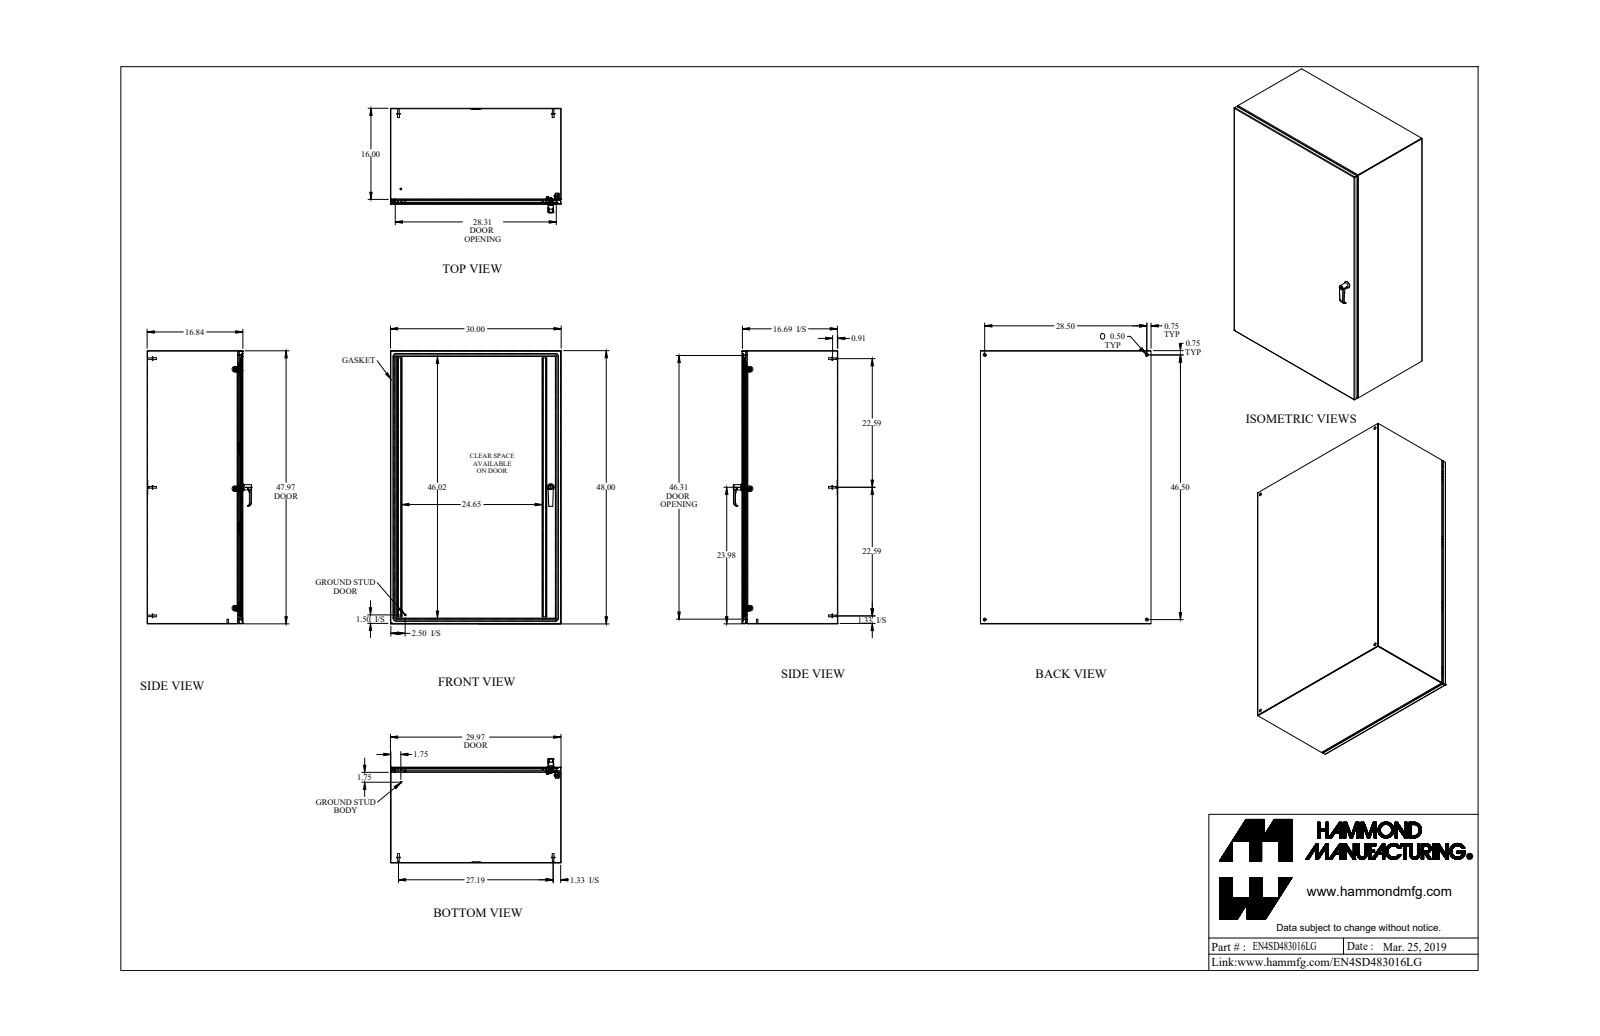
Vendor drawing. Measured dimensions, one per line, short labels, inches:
name: EN4SD483016LG
written by: SolidWorks 2018 (AUTOMOTIVE_DESIGN)
unit: in
bodies: 54 solids, 1427 faces (628 planar, 526 cylindrical, 273 other)
size: 48 × 30 × 18.367
volume: 439.2 in³; area: 12 206 in²
holes: 6× ⌀0.176, 4× ⌀0.5, 3× ⌀0.196, 3× ⌀0.25, 3× ⌀0.265, 3× ⌀0.413, 2× ⌀0.256, 2× ⌀0.313, 2× ⌀0.394, 1× ⌀0.172, 1× ⌀0.24, 1× ⌀0.242
bosses: 7× ⌀0.25, 6× ⌀0.375, 6× ⌀0.156, 5× ⌀0.625, 5× ⌀0.313, 5× ⌀0.27, 3× ⌀1, 2× ⌀0.63
rounds: 18× R0.036, 18× R0.108, 15× R0.03, 12× R0.043, 12× R0.081, 8× R0.006, 8× R0.048, 8× R0.062
face distances: 0.072, 16.765, 29.928, 16.693, 16.837, 29.856, 30, 0.072, 47.856, 47.928
hole spacings: 41.969, 0.787, 20.981, 20.988, 21, 27.52, 28.5, 46.5
